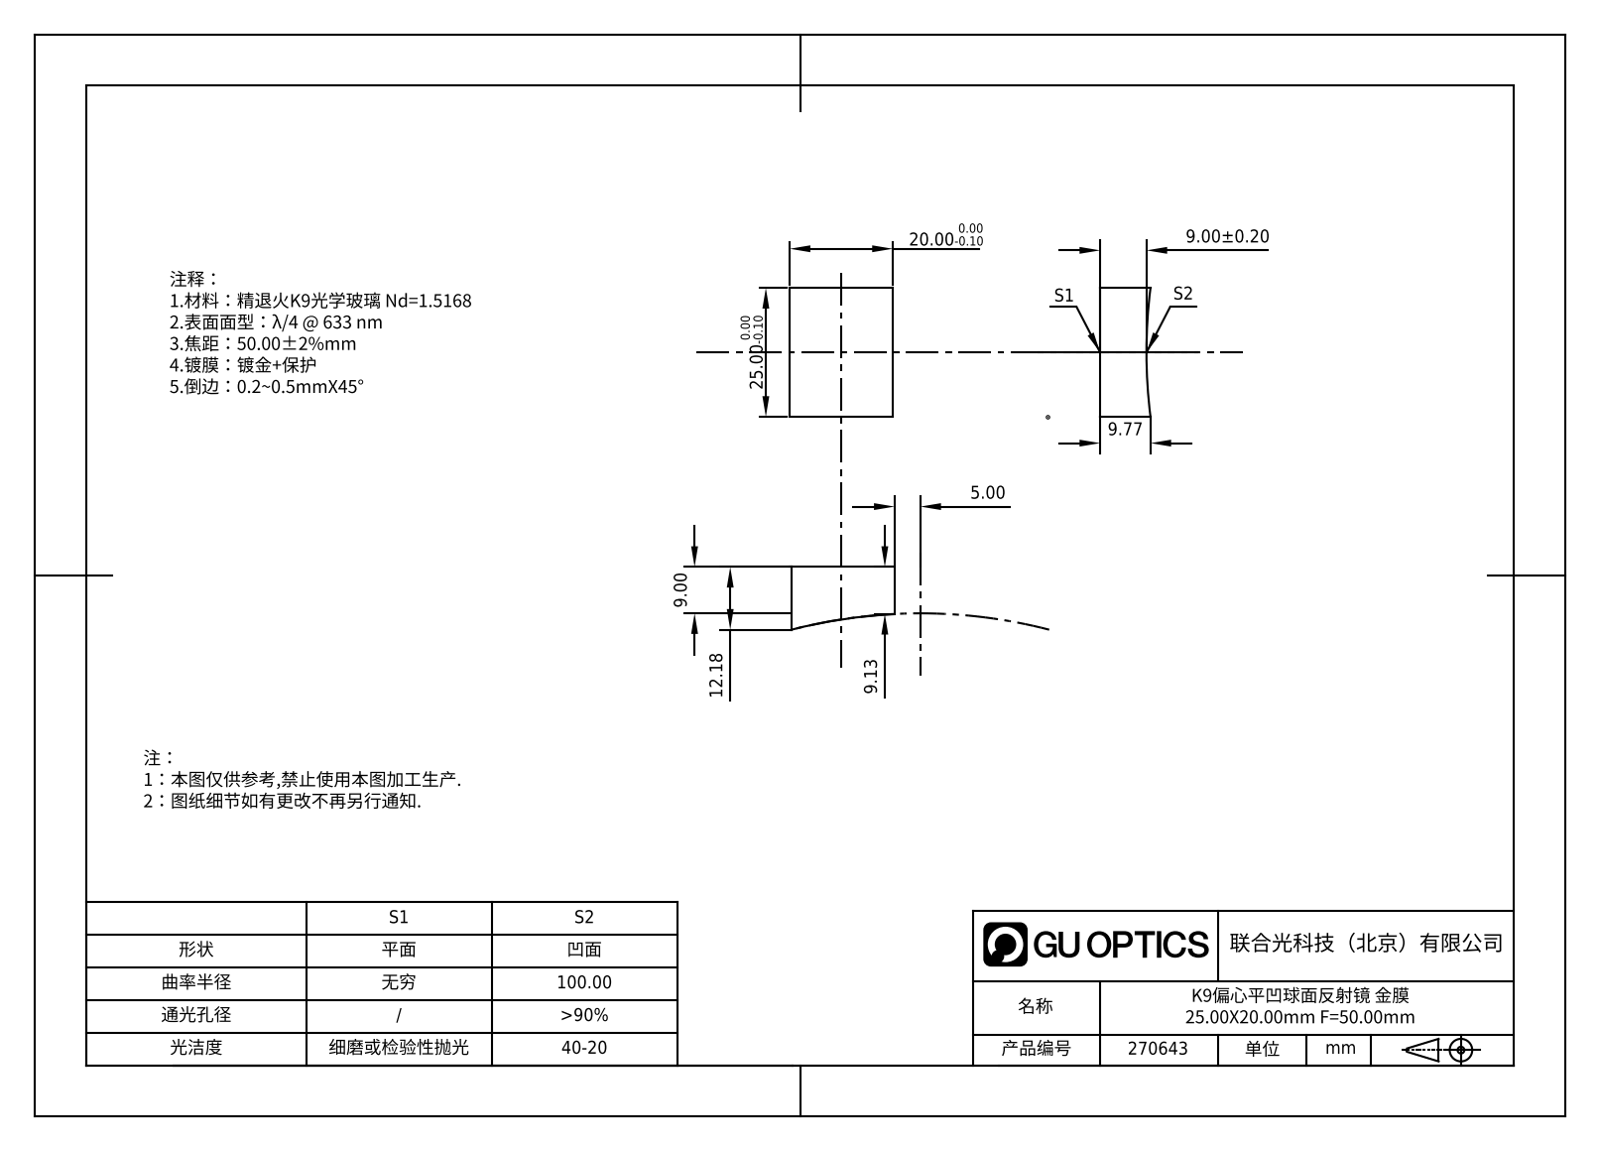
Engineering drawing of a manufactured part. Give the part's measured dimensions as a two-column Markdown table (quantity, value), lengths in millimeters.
| quantity | value |
| --- | --- |
| part name | 270643 |
| STEP written by | SolidWorks 2020 (CONFIG_CONTROL_DESIGN) |
| units | millimeters |
| bodies | 1 solid, 7 faces (5 planar, 0 cylindrical, 2 other) |
| overall size | 25 × 20 × 12.99 |
| volume | 5 284 mm³ |
| surface area | 1 998 mm² |
| main face-to-face distances | 20, 25 |
